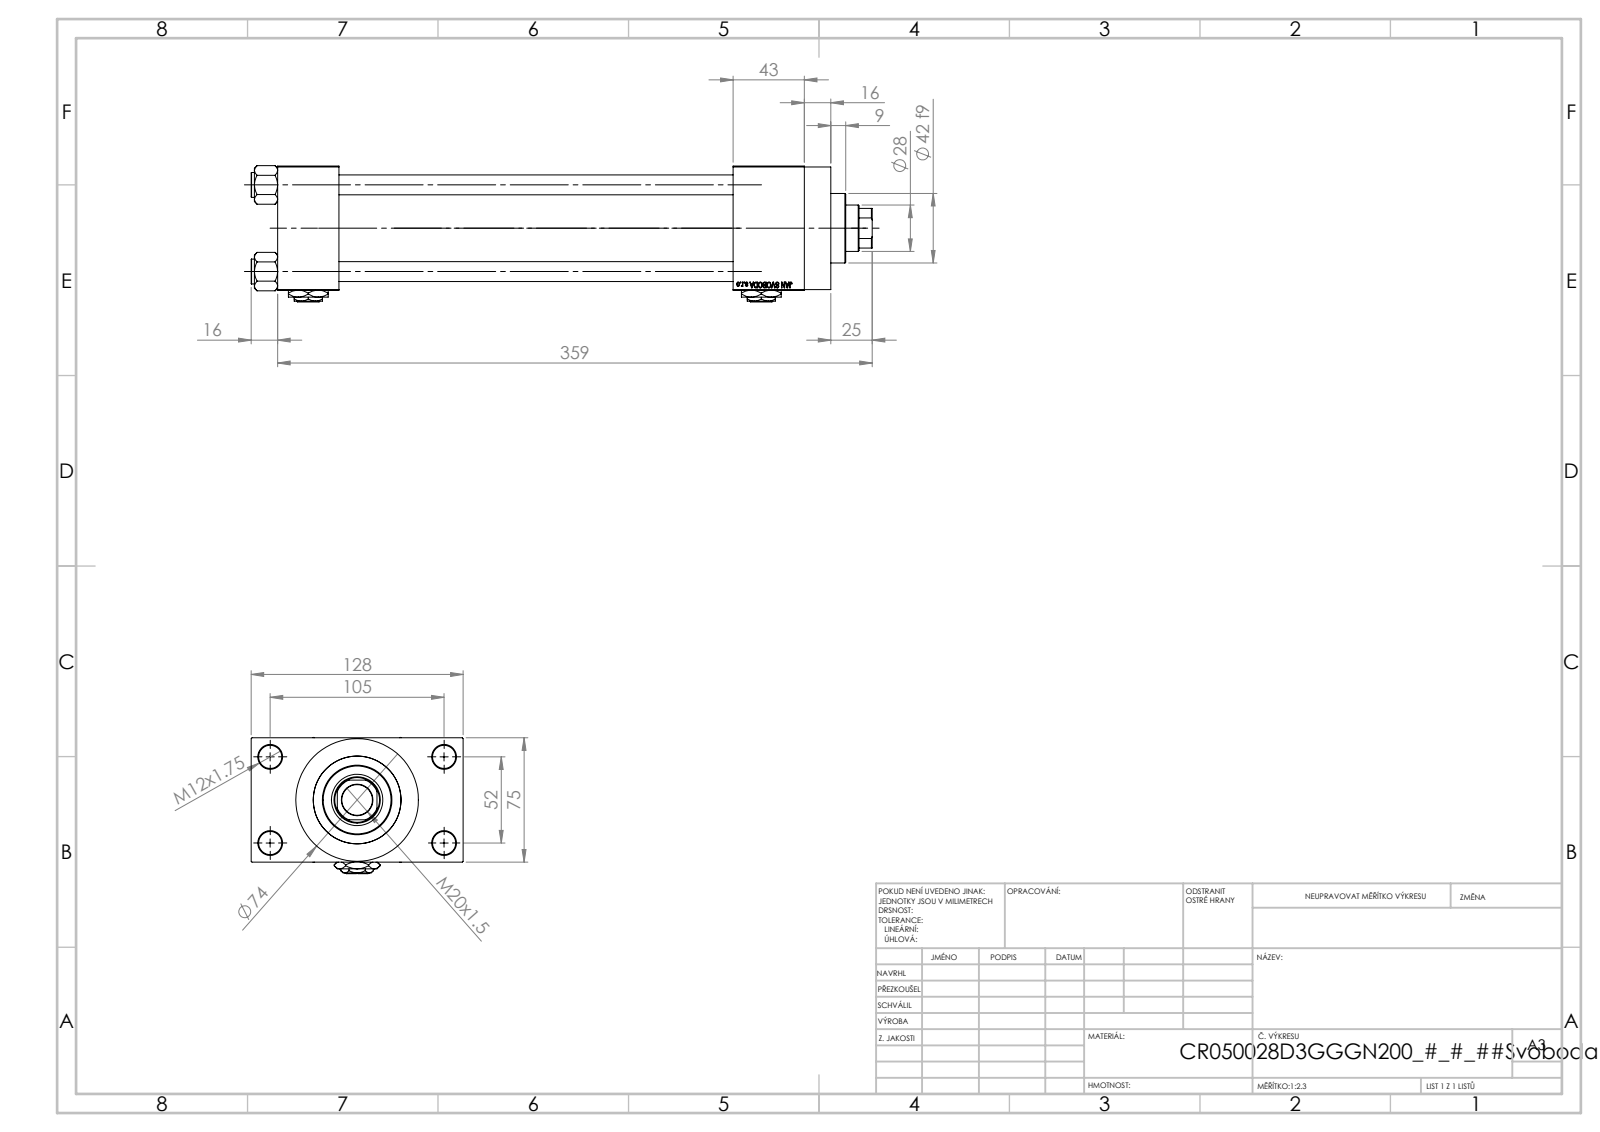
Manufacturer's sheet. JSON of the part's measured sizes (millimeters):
{"part_name": "V215CR_D_TYCINKA; V215CR_VCP_D; V215_VC_A; NUT_M5_D (+2 more)", "step_written_by": "SolidWorks 2019 (CONFIG_CONTROL_DESIGN)", "units": "millimeters", "bodies": {"solids": 13, "faces": 1205, "planar": 545, "cylindrical": 100, "other": 560}, "overall_size": [375, 128, 82.27], "volume_mm3": 1093000, "surface_area_mm2": 276023, "round_holes": [[12, 4], [14, 4], [7, 2], [20.96, 2], [30, 2], [18.5, 1], [28, 1], [31, 1], [41, 1], [50, 1], [53, 1]], "round_bosses_or_shafts": [[15, 4], [74, 1], [56, 1], [42, 1]], "partial_cylinders_radius": [[13.5, 1]], "face_to_face_distances": [75, 238, 37, 275, 26.5, 101.5, 318, 281, 43, 16], "hole_center_spacings": [26.35, 36.98, 52.3, 58.43, 58.59, 78.65, 94.37, 52]}
